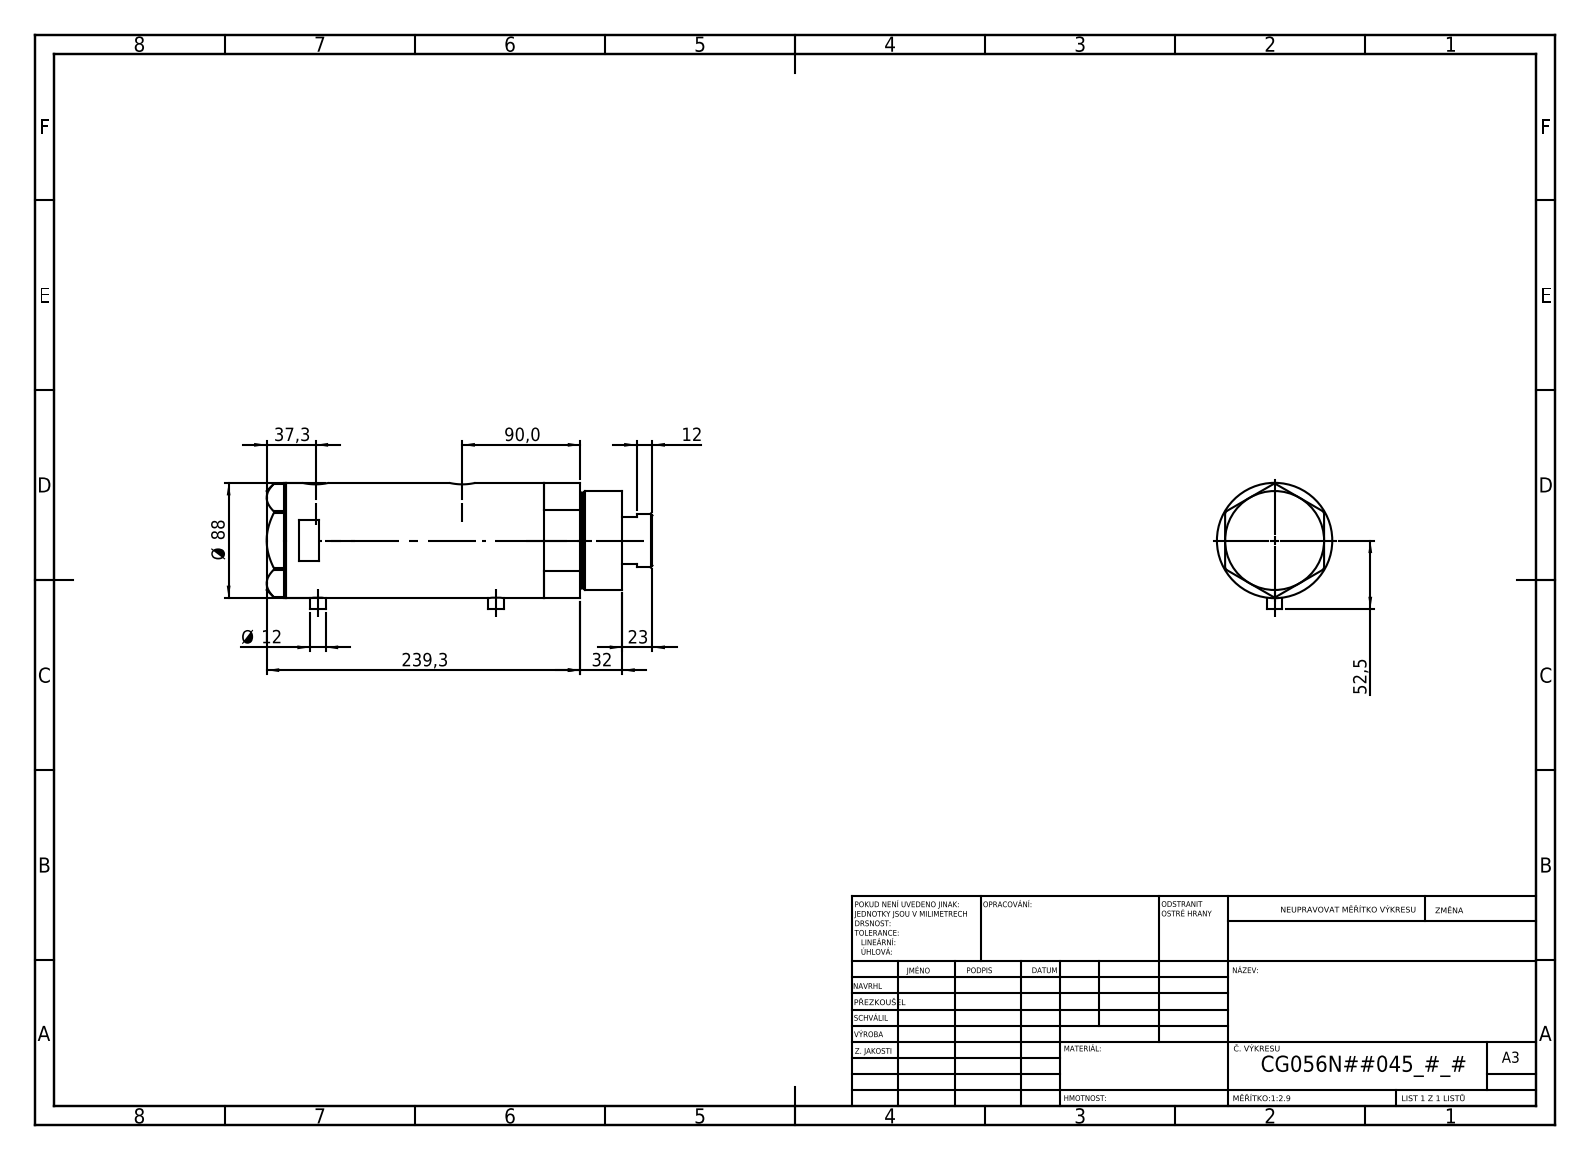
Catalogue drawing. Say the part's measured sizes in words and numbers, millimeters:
The part is named "V270CG_MIDDLE; V270CG_VC; V270CG_FRONT; V270CG_BACK". Its 3-D file was written by "SolidWorks 2019 (CONFIG_CONTROL_DESIGN)". It is 4 solids with 121 faces: 52 planar, 49 cylindrical and 20 other. Overall it measures 294.3 by 96.5 by 88 millimeters. Its volume is 1 539 000 cubic millimeters and its surface area 221 654 square millimeters. Round holes: 2 of diameter 12.5, 2 of diameter 13.16, 2 of diameter 20, 1 of diameter 14.5, 1 of diameter 42, 1 of diameter 43.5, 1 of diameter 56, 1 of diameter 60, 1 of diameter 80. Round bosses or shafts: 2 of diameter 12, 1 of diameter 88, 1 of diameter 75, 1 of diameter 73, 1 of diameter 41. The main face-to-face distances are 134.4, 26, 108.4, 15, 41, 149.4, 256.3, 271.3, 230.3, 121.9. The hole center spacings are 1.7, 25.8, 110.3, 112, 136.1, 137.8.
